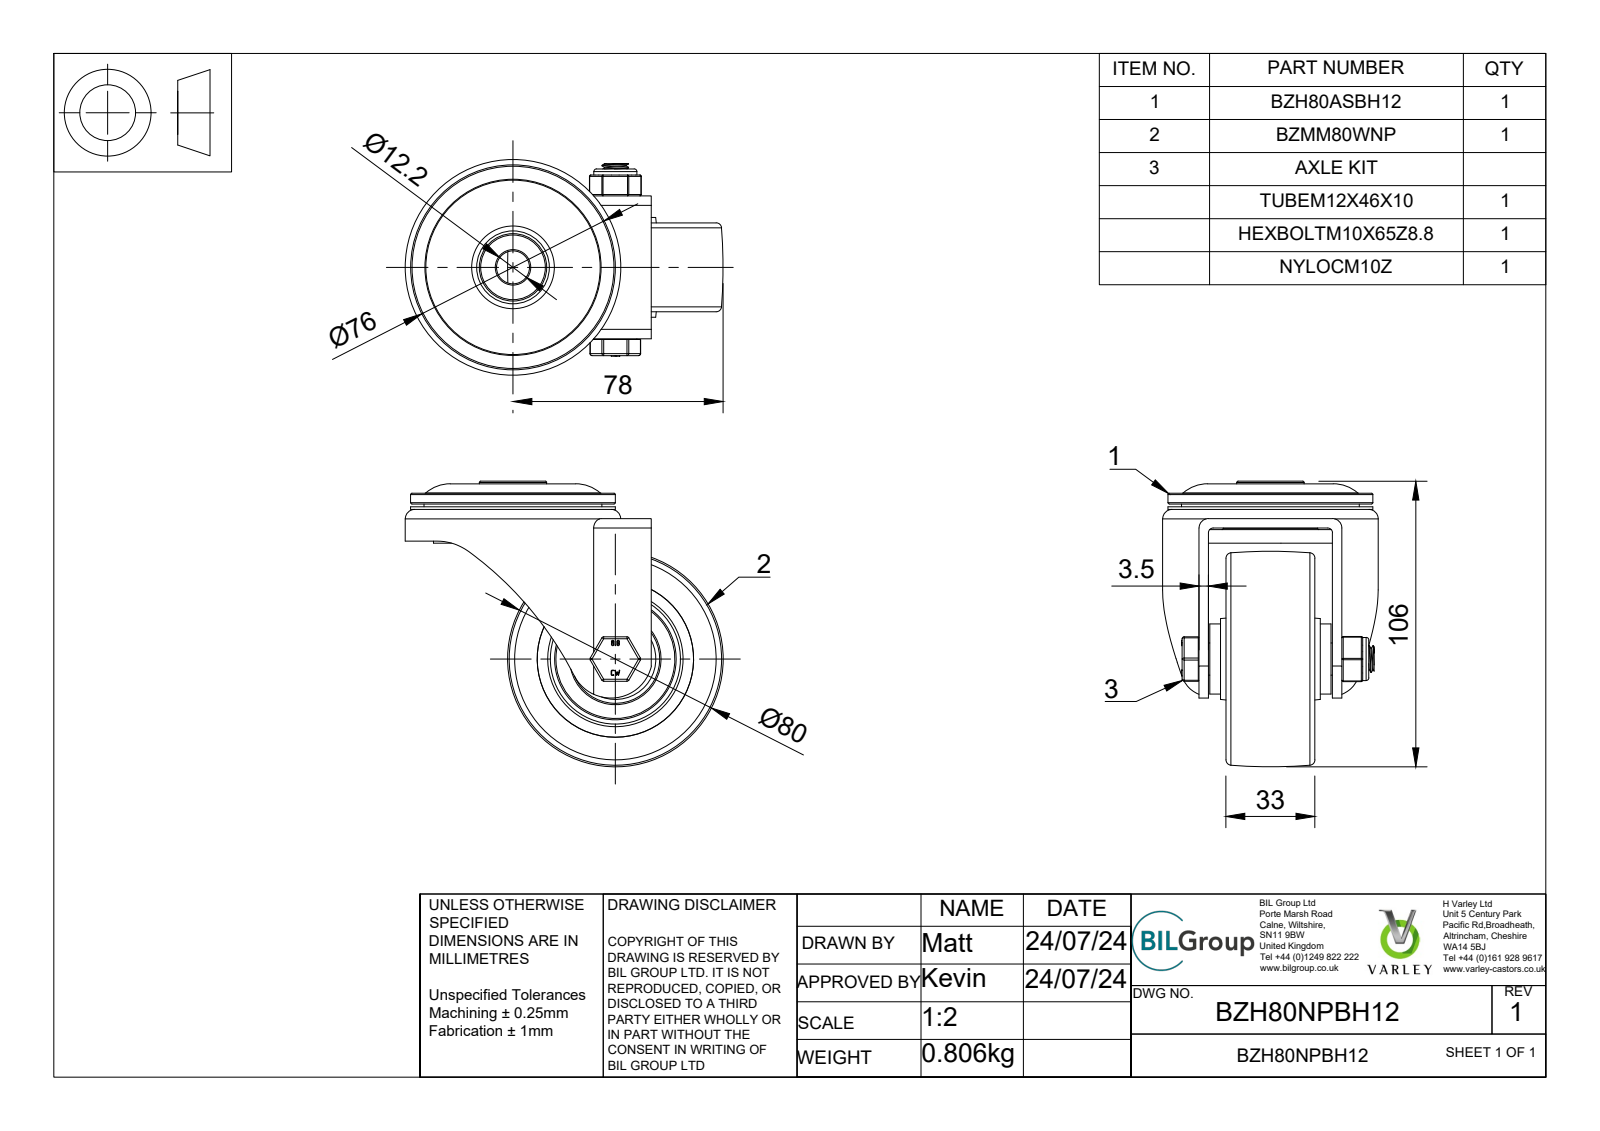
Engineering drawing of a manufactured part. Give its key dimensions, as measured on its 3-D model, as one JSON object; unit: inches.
{"part_name": "BZH80NPBH12 v3; BZH80ASBH12 v1; ZINC PLATED, PRESSED STEEL TOP PLATE; ZINC PLATED, PRESSED STEEL TOP PLATE Geometry (+7 more)", "step_written_by": "Autodesk Translation Framework v13.14.0.145 (AUTOMOTIVE_DESIGN)", "units": "inches", "bodies": {"solids": 25, "faces": 376, "planar": 104, "cylindrical": 161, "other": 111}, "overall_size": [4.646, 4.173, 3.15], "volume_in3": 14.29, "surface_area_in2": 151.5, "round_holes": [[2.283, 2], [0.394, 1], [0.402, 1], [0.472, 1], [0.48, 1], [0.492, 1], [1.299, 1], [2.874, 1]], "round_bosses_or_shafts": [[3.15, 1], [2.992, 1], [2.598, 1], [2.323, 1], [1.378, 1], [1.024, 1], [0.984, 1], [0.866, 1]], "partial_cylinders_radius": [[0.02, 18], [0.03, 12], [0.069, 4], [0.138, 2], [0.605, 1], [0.787, 1], [5.125, 1]], "face_to_face_distances": [0.138, 0.157, 0.531, 0.374, 0.197, 0.236, 0.079, 1.693, 0.256, 0.394]}
